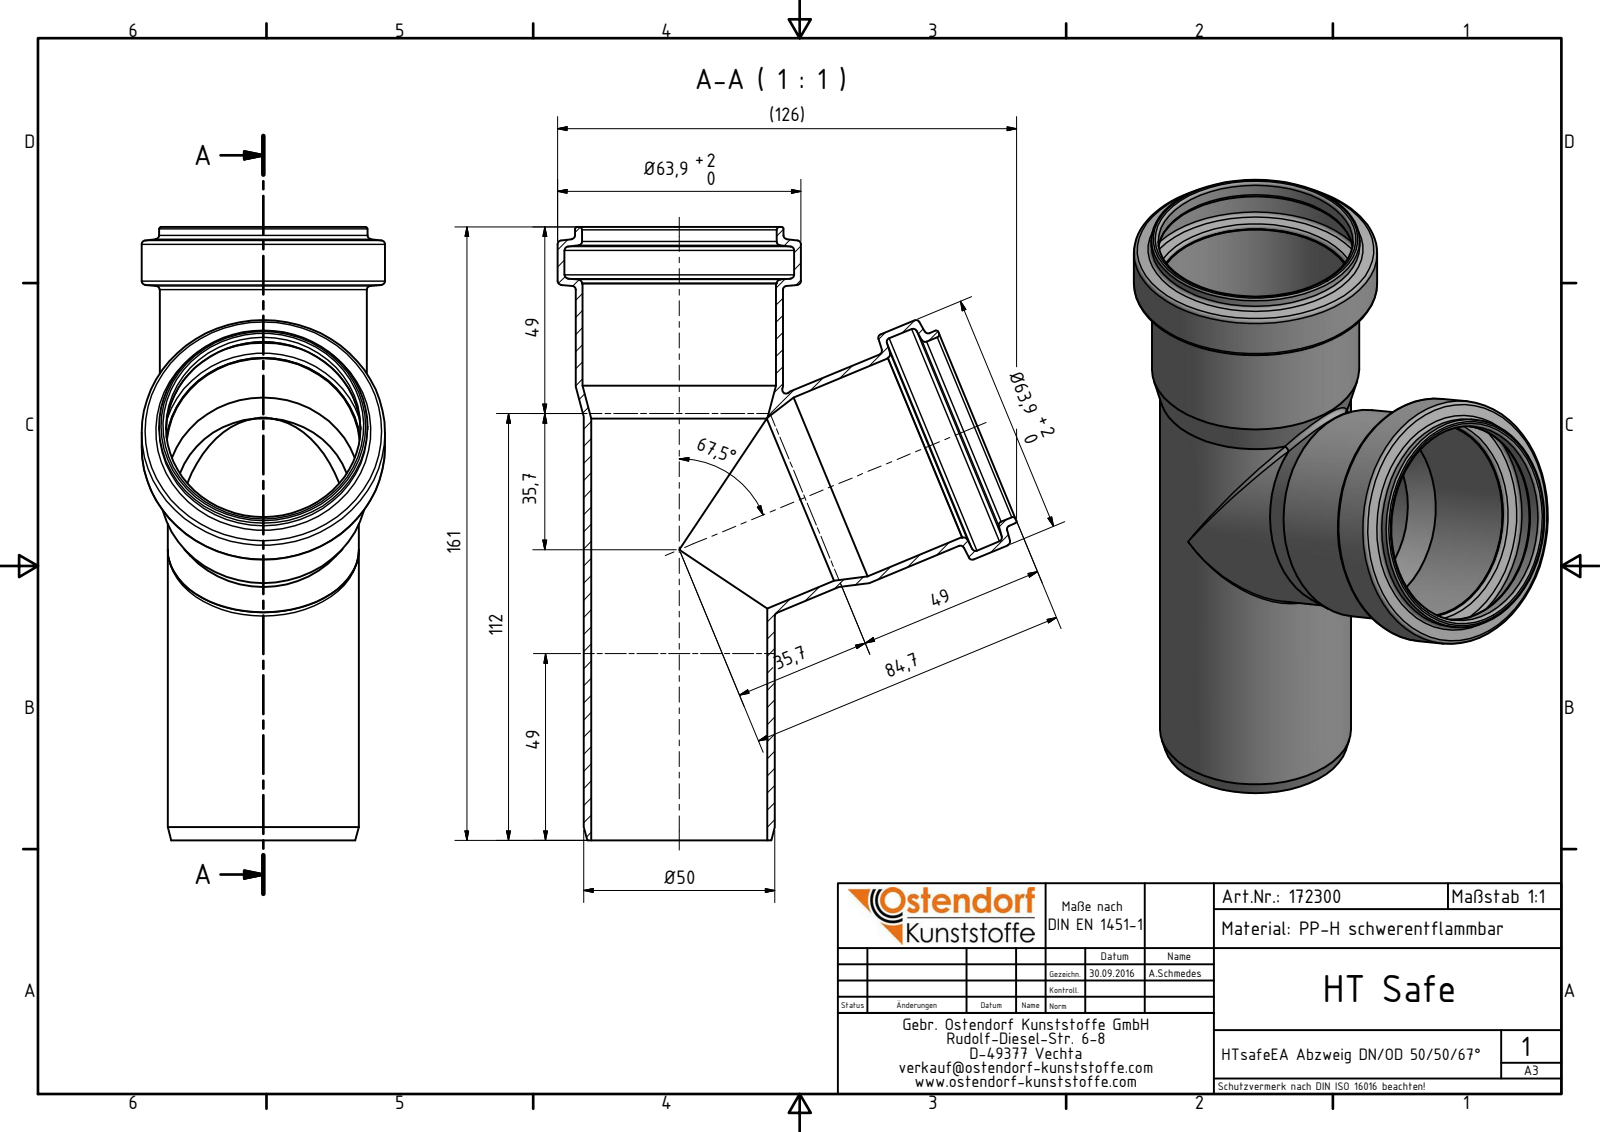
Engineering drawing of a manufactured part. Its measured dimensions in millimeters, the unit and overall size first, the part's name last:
Units: millimetres
Overall size (bounding box): 161 × 120.52 × 63.9
Round holes (diameter × count): ⌀51.1 ×3, ⌀46.2 ×2, ⌀50.8 ×2, ⌀60.3 ×2
Round bosses / shafts (diameter × count): ⌀63.9 ×2, ⌀54.7 ×2, ⌀54.4 ×2, ⌀50.2 ×2
Main face-to-face distances: 161, 14.9, 146.1
Volume: 70 003 mm³ · Surface area: 73 874 mm²
Bodies: 1 solid, 60 faces (5 planar, 18 cylindrical, 37 other)
Part name (STEP PRODUCT): 172300 HTsafeEA DN_OD 50_50_67°
STEP written by: Autodesk Inventor 2016 (AUTOMOTIVE_DESIGN)
